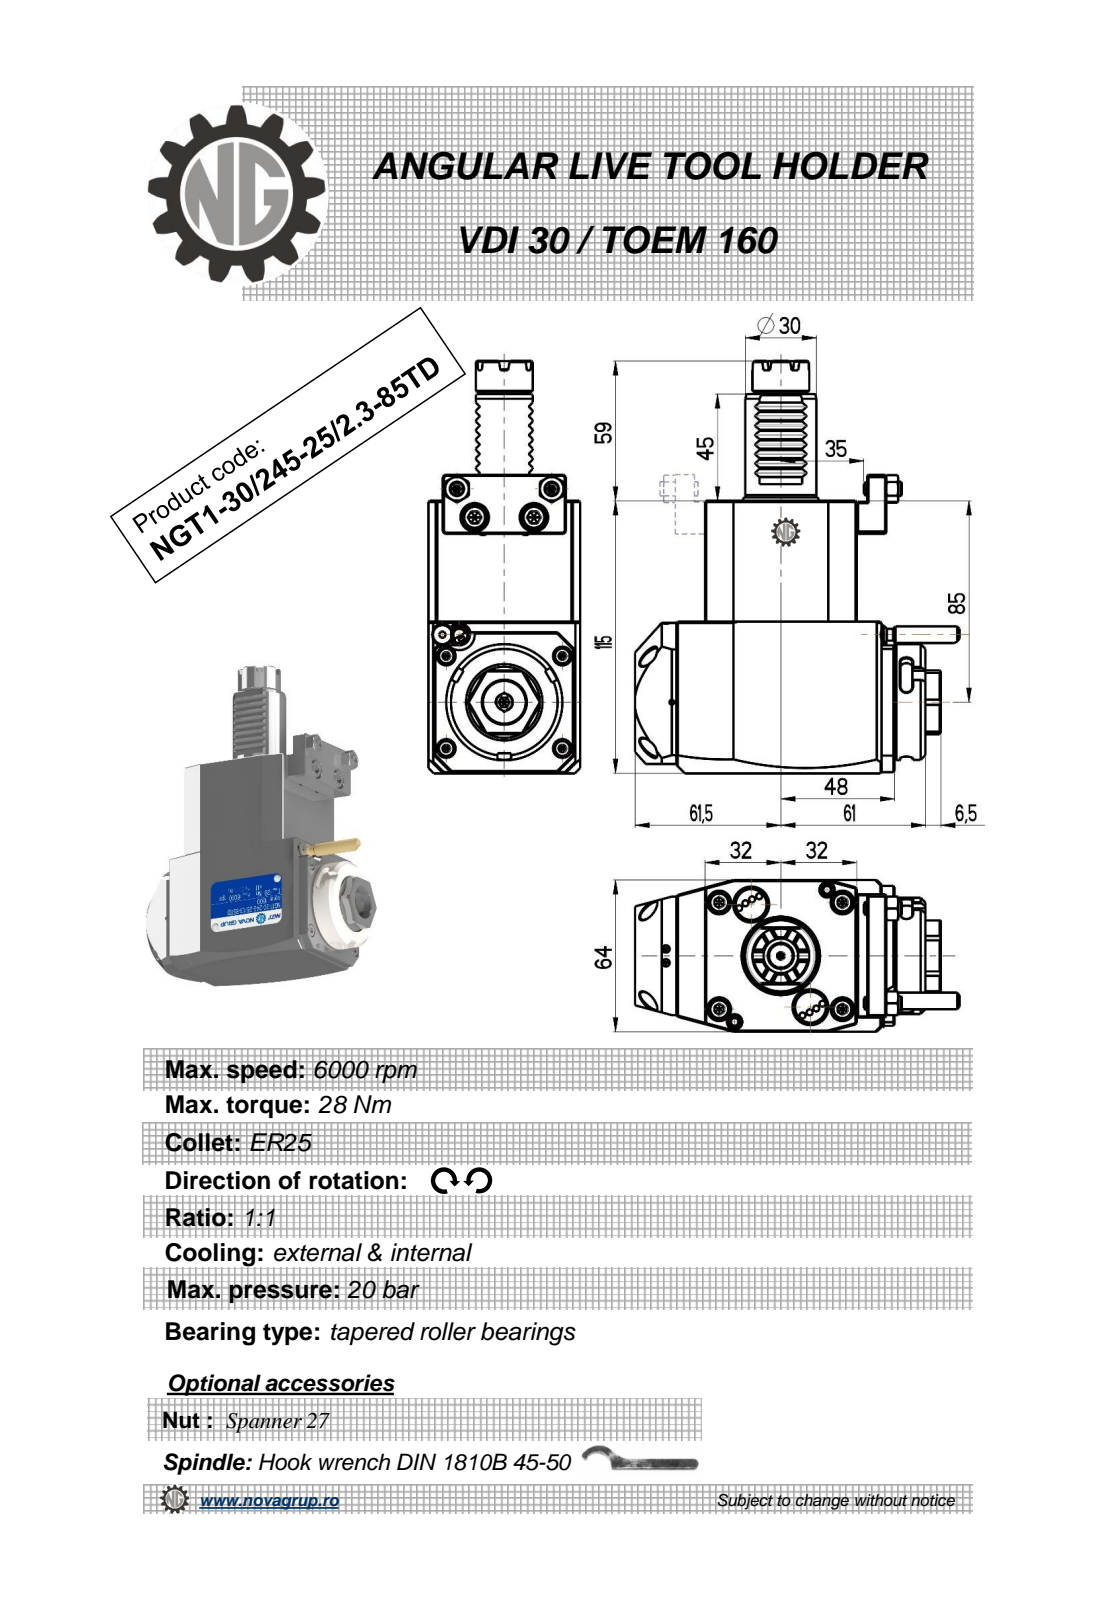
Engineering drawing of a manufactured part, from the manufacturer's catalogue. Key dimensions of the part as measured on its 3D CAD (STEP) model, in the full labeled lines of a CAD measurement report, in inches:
Part name (STEP PRODUCT): NGT1_30_245_25_1_3_85TD
STEP written by: PRO/ENGINEER BY PARAMETRIC TECHNOLOGY CORPORATION, 2010280 (CONFIG_CONTROL_DESIGN)
Units: inches
Bodies: 1 solid, 425 faces (237 planar, 80 cylindrical, 108 other)
Overall size (bounding box): 6.85 × 5.389 × 2.52
Volume: 41.52 in³ · Surface area: 91.81 in²
Round holes (diameter × count): ⌀0.098 ×1, ⌀0.118 ×1, ⌀0.709 ×1
Round bosses / shafts (diameter × count): ⌀0.236 ×2, ⌀1.929 ×1, ⌀1.654 ×1, ⌀1.181 ×1, ⌀0.945 ×1, ⌀0.697 ×1, ⌀0.598 ×1, ⌀0.315 ×1
Partial cylindrical surfaces — rounded edges, fillets, slot ends (radius × count): R0.012 ×16, R0.012 ×10, R0.098 ×6, R7.087 ×2, R0.177 ×1, R0.591 ×1, R0.846 ×1, R1.319 ×1
Main face-to-face distances: 2.52, 4.528, 0.63, 0.512, 3.15, 0.138, 0.65, 0.492, 2.008, 0.236
Hole centre spacings: 1.348
